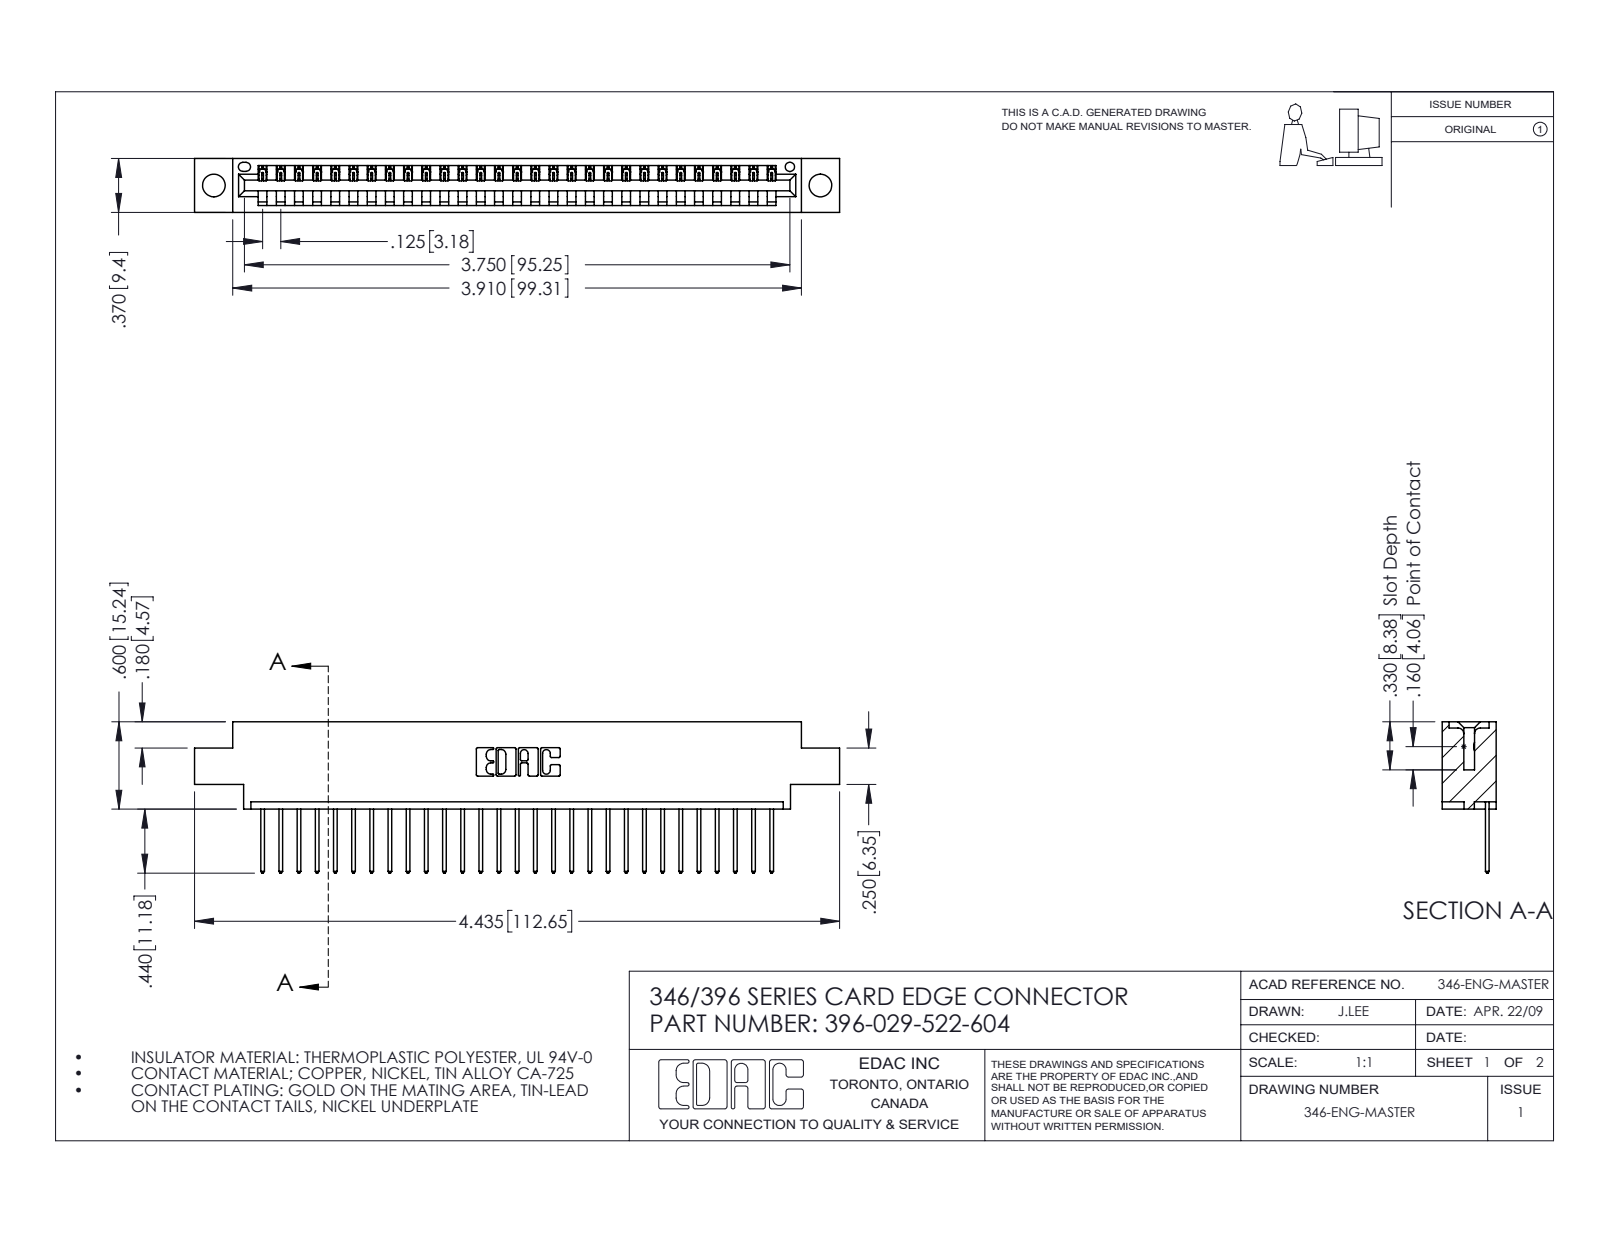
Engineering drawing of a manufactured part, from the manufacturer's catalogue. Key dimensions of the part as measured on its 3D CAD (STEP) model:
Part name (STEP PRODUCT): 346 Part_0.170 Offset - 0.156 Dia-TH; 345-292-001_345-293-122; 396-029-522-604
STEP written by: SolidWorks 2016 (CONFIG_CONTROL_DESIGN)
Units: inches
Bodies: 30 solids, 1808 faces (1240 planar, 568 cylindrical, 0 other)
Overall size (bounding box): 4.435 × 1.04 × 0.37
Volume: 0.638 in³ · Surface area: 20.15 in²
Round holes (diameter × count): ⌀0.156 ×2, ⌀0.064 ×1
Partial cylindrical surfaces — rounded edges, fillets, slot ends (radius × count): R0.006 ×58, R0.01 ×58, R0.01 ×22, R0.007 ×6, R0.031 ×6, R0.026 ×3, R0.031 ×2, R0.04 ×2
Main face-to-face distances: 0.048, 0.322, 0.37, 0.25, 0.072, 0.298, 0.025, 0.148, 0.222, 0.1
Hole centre spacings: 0.246, 3.962, 4.17
